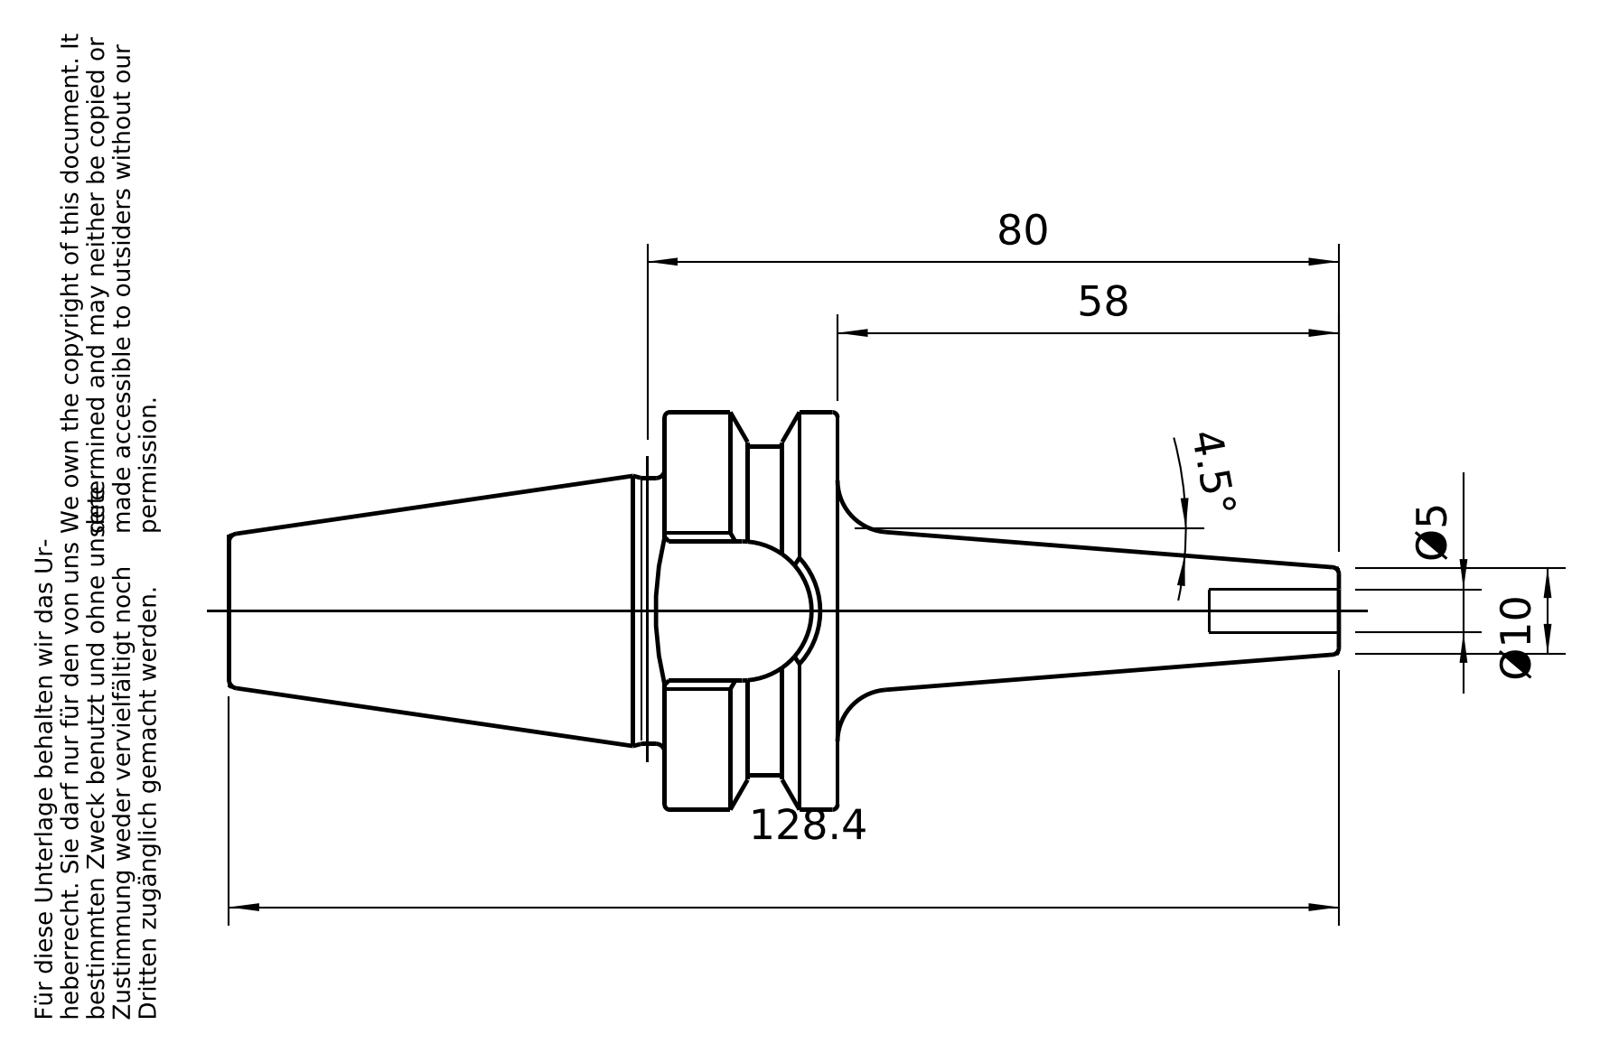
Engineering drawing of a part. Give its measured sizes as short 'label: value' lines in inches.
name: 30-640-05
written by: PRO/ENGINEER BY PARAMETRIC TECHNOLOGY CORPORATION, 2010430 (CONFIG_CONTROL_DESIGN)
unit: in
bodies: 1 solid, 94 faces (26 planar, 20 cylindrical, 48 other)
size: 5.055 × 1.81 × 1.81
volume: 3.639 in³; area: 22.34 in²
holes: 1× ⌀0.197, 1× ⌀0.398, 1× ⌀0.493, 1× ⌀0.512
bosses: 1× ⌀1.81, 1× ⌀1.211, 1× ⌀0.473
rounds: 1× R0.319, 1× R0.743
face distances: 0.787, 1.272, 0.638, 1.984, 2.772, 5.055, 3.071, 2.283, 0.984, 1
